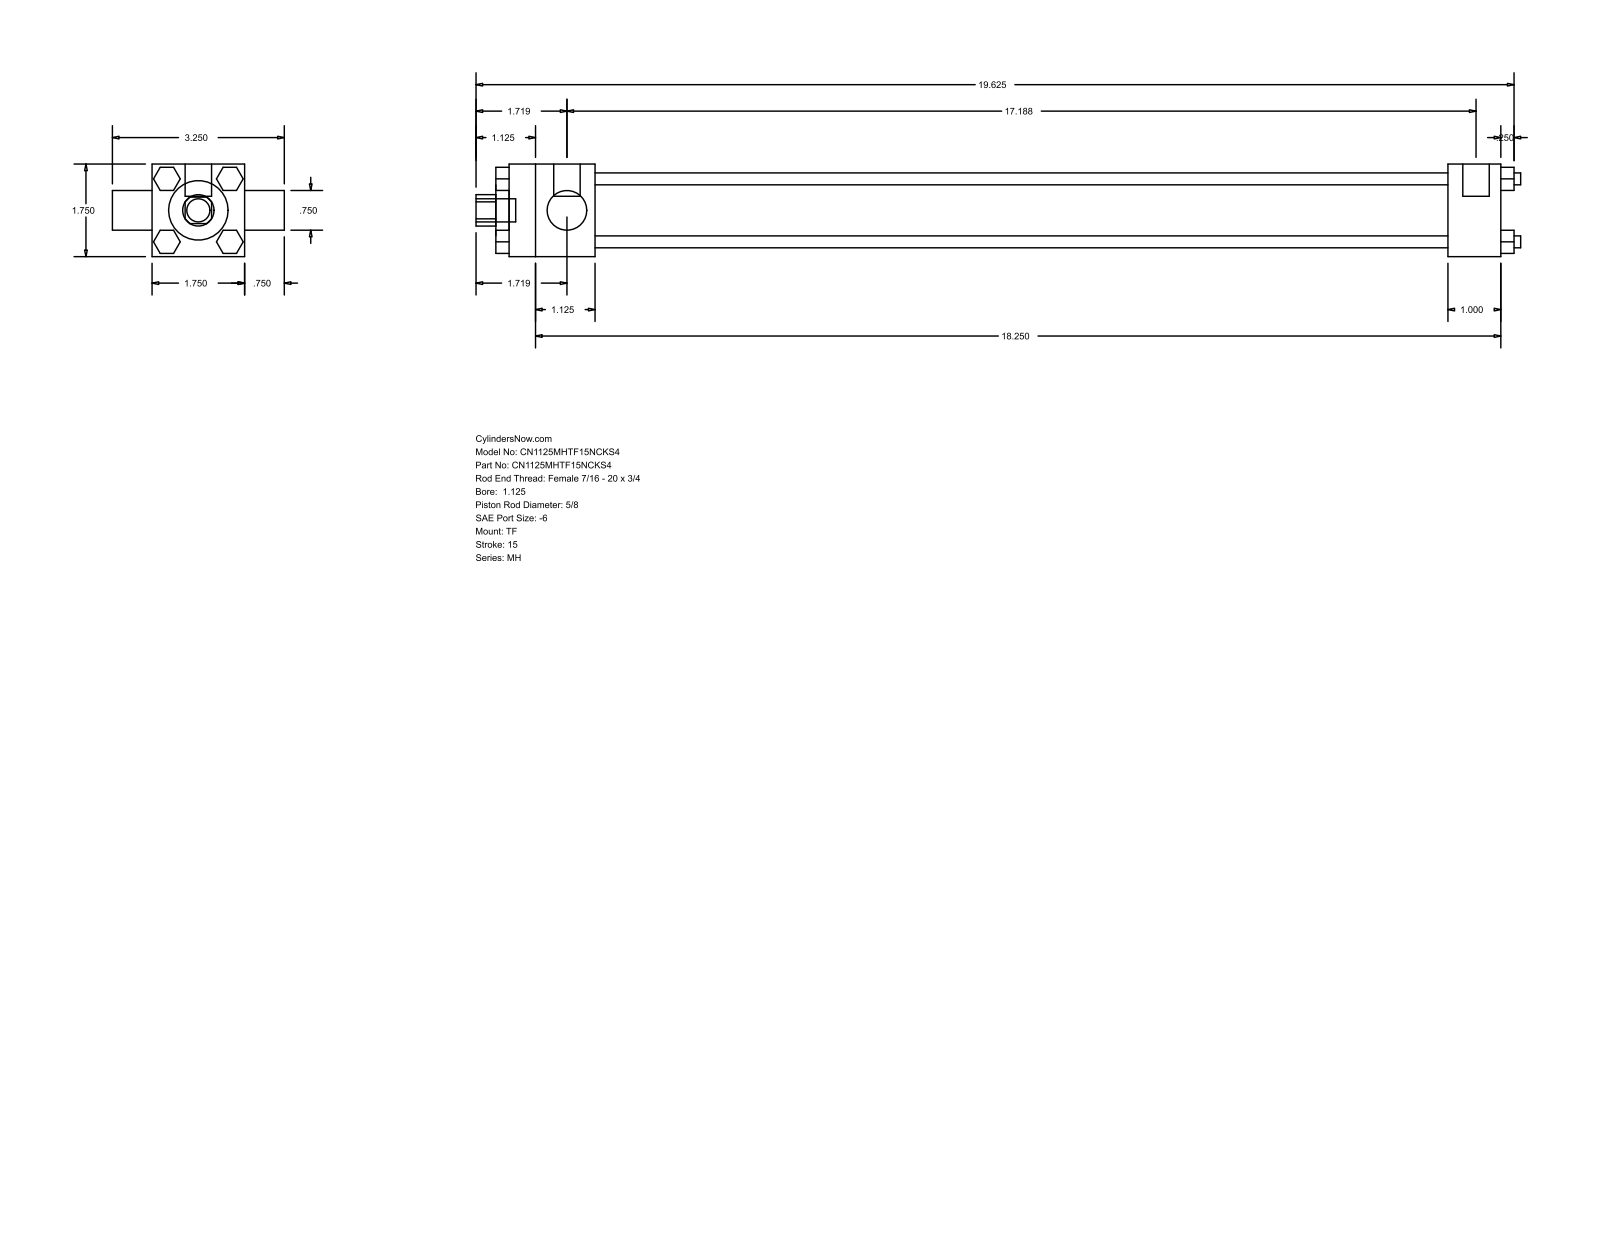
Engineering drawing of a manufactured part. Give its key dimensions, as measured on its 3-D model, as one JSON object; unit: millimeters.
{"part_name": "MH_TF__0112_0.625", "step_written_by": "GSSL Pune (CONFIG_CONTROL_DESIGN)", "units": "millimeters", "bodies": {"solids": 0, "faces": 120, "planar": 92, "cylindrical": 28, "other": 0}, "overall_size": [501.65, 82.55, 44.45], "round_holes": [[15.88, 1], [19.05, 1], [28.57, 1], [34.92, 1]], "round_bosses_or_shafts": [[5.71, 4], [5.56, 3], [12.7, 2], [11.11, 1]], "partial_cylinders_radius": [[7.54, 1]], "face_to_face_distances": [44.46, 11.11, 409.58, 434.97, 25.39, 41.27, 450.85, 476.24, 47.62, 6.35]}
